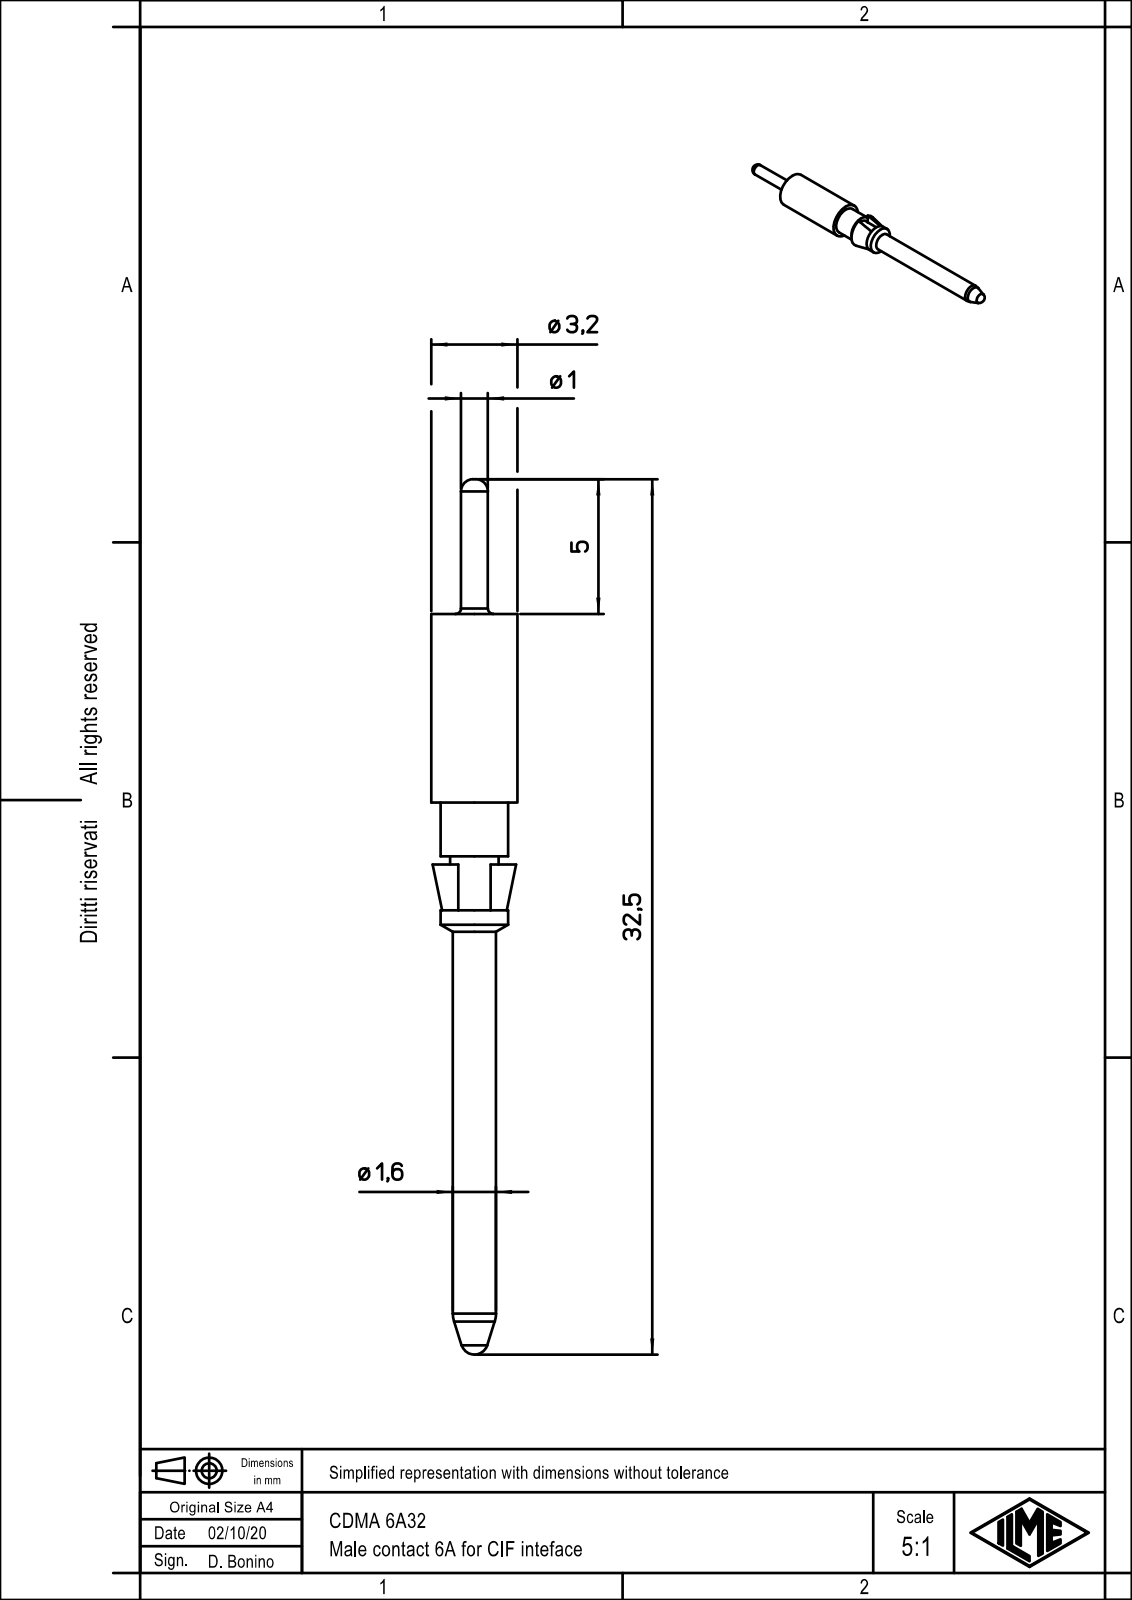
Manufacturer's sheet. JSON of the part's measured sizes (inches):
{"part_name": "CDMA_6A32", "step_written_by": "Creo Elements/Direct Modeling 20.1B 02-Apr-2019 (C) Parametric Technology GmbH (AUTOMOTIVE_DESIGN)", "units": "inches", "bodies": {"solids": 1, "faces": 33, "planar": 8, "cylindrical": 12, "other": 13}, "overall_size": [1.28, 0.126, 0.126], "volume_in3": 0.008, "surface_area_in2": 0.366, "round_bosses_or_shafts": [[0.126, 1], [0.098, 1], [0.071, 1], [0.063, 1], [0.039, 1]], "face_to_face_distances": [0.465, 0.091, 0.374, 0.079, 0.453, 0.047, 0.067, 0.157, 0.531, 0.728]}
